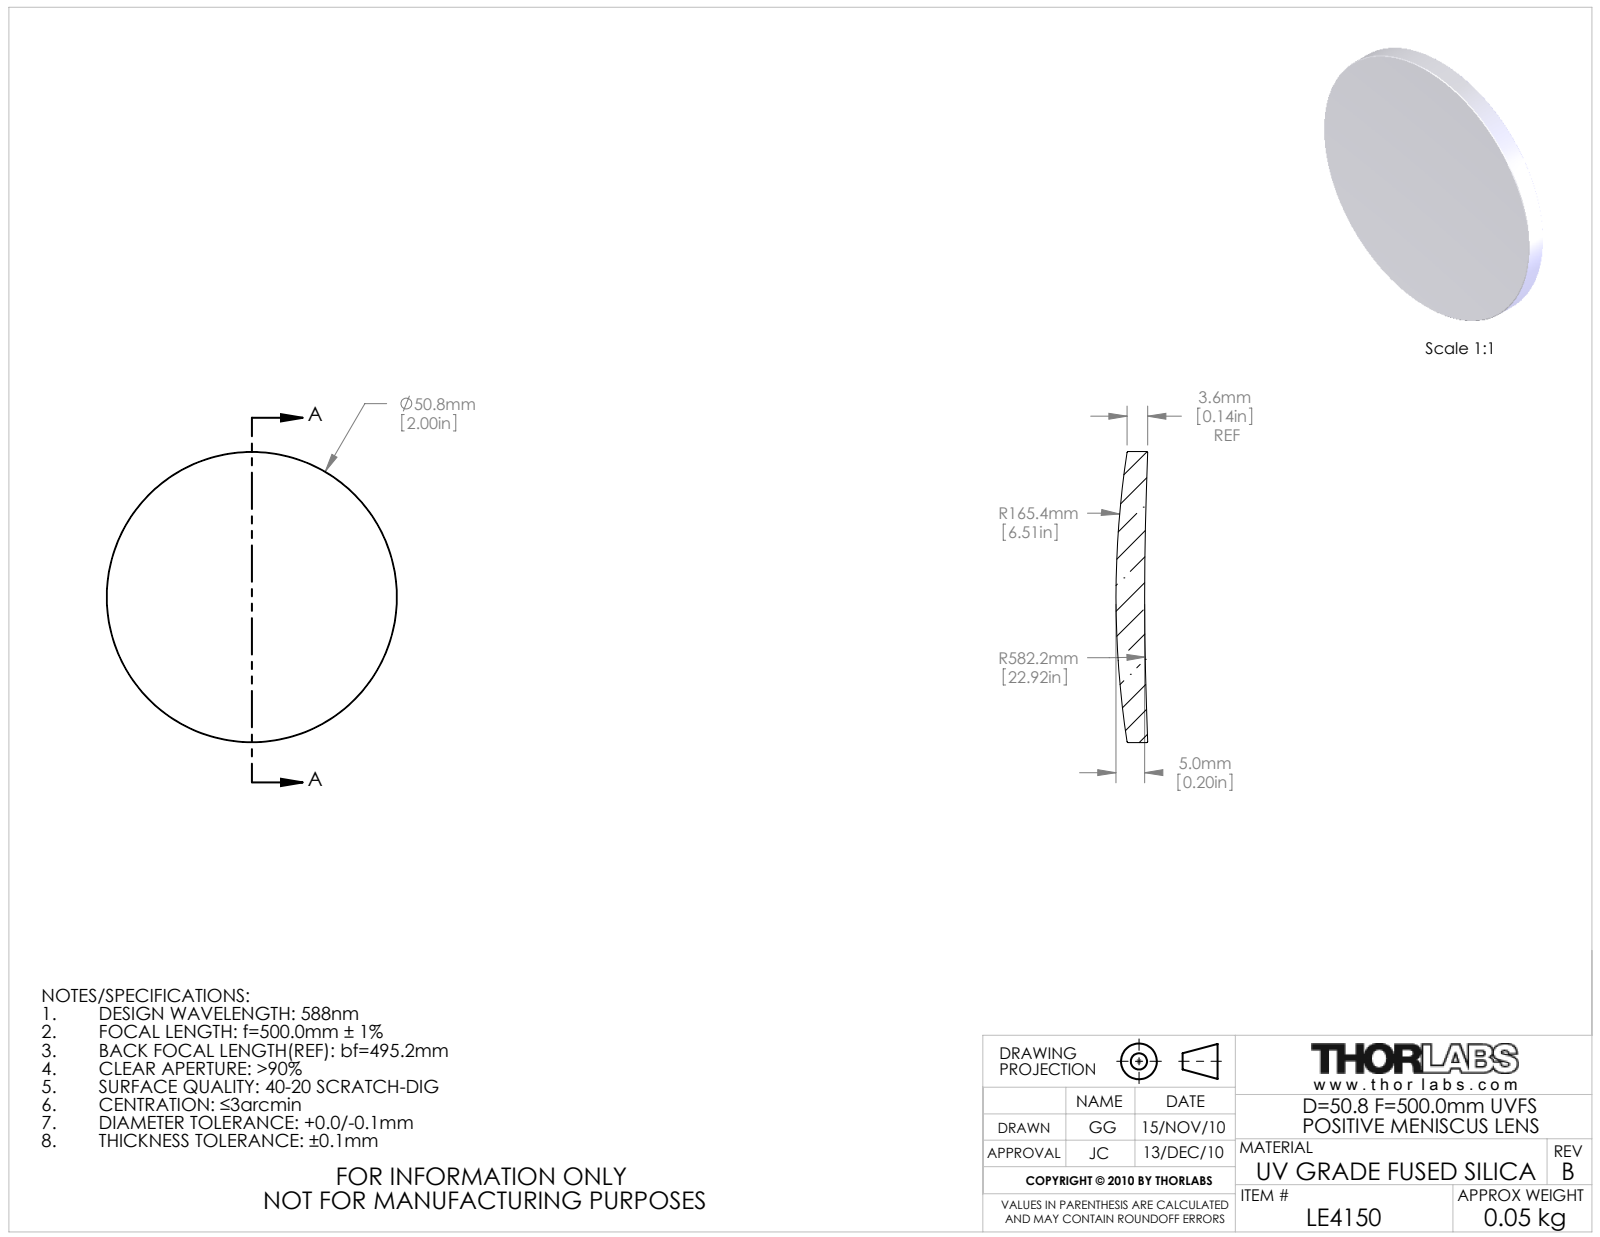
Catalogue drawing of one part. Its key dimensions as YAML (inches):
part_name: "4216-E0W"
step_written_by: "SolidWorks 2009 (AUTOMOTIVE_DESIGN)"
units: inches
bodies: {solids: 1, faces: 10, planar: 0, cylindrical: 2, other: 8}
overall_size: [2, 2, 0.219]
volume: 0.531
surface_area: 7.155
round_bosses_or_shafts:
  - {diameter: 2, count: 1}
